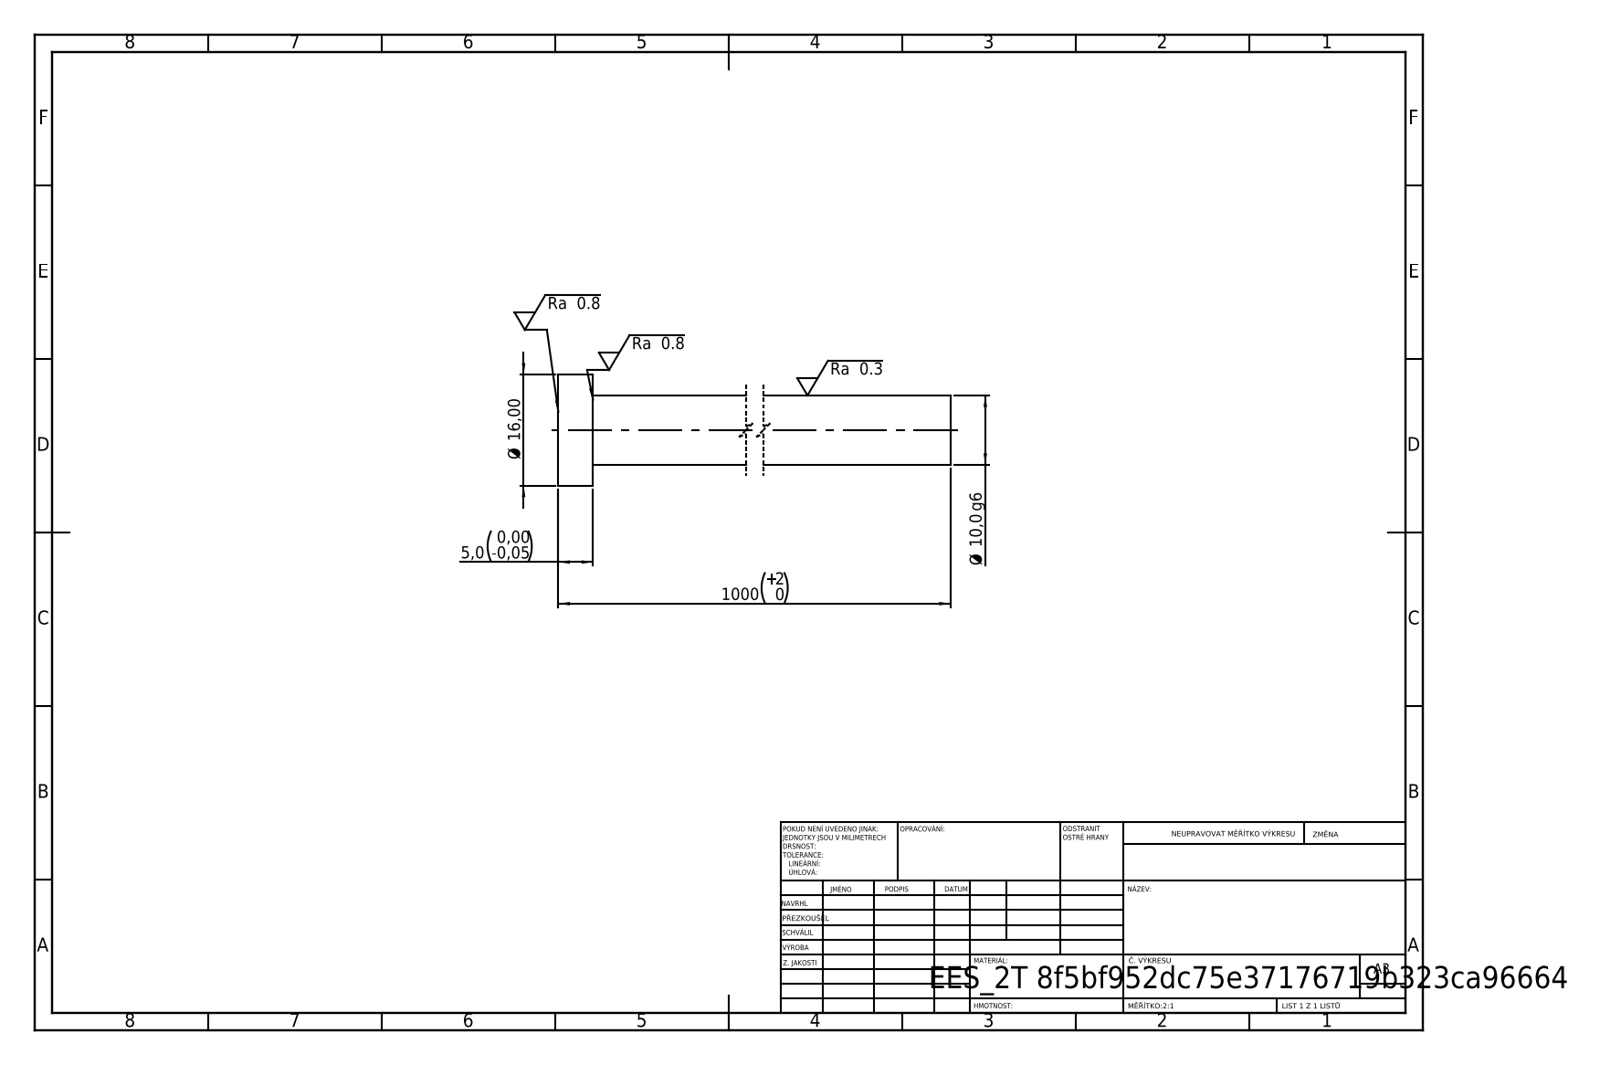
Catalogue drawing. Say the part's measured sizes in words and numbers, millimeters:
Its 3-D file was written by "SolidWorks 2019 (CONFIG_CONTROL_DESIGN)". It is 1 solid with 7 faces: 3 planar, 4 cylindrical and 0 other. Overall it measures 1000 by 16 by 16 millimeters. Its volume is 79 152 cubic millimeters and its surface area 31 912 square millimeters. Round bosses or shafts: 1 of diameter 16, 1 of diameter 10. The main face-to-face distances are 5, 1000, 995.
